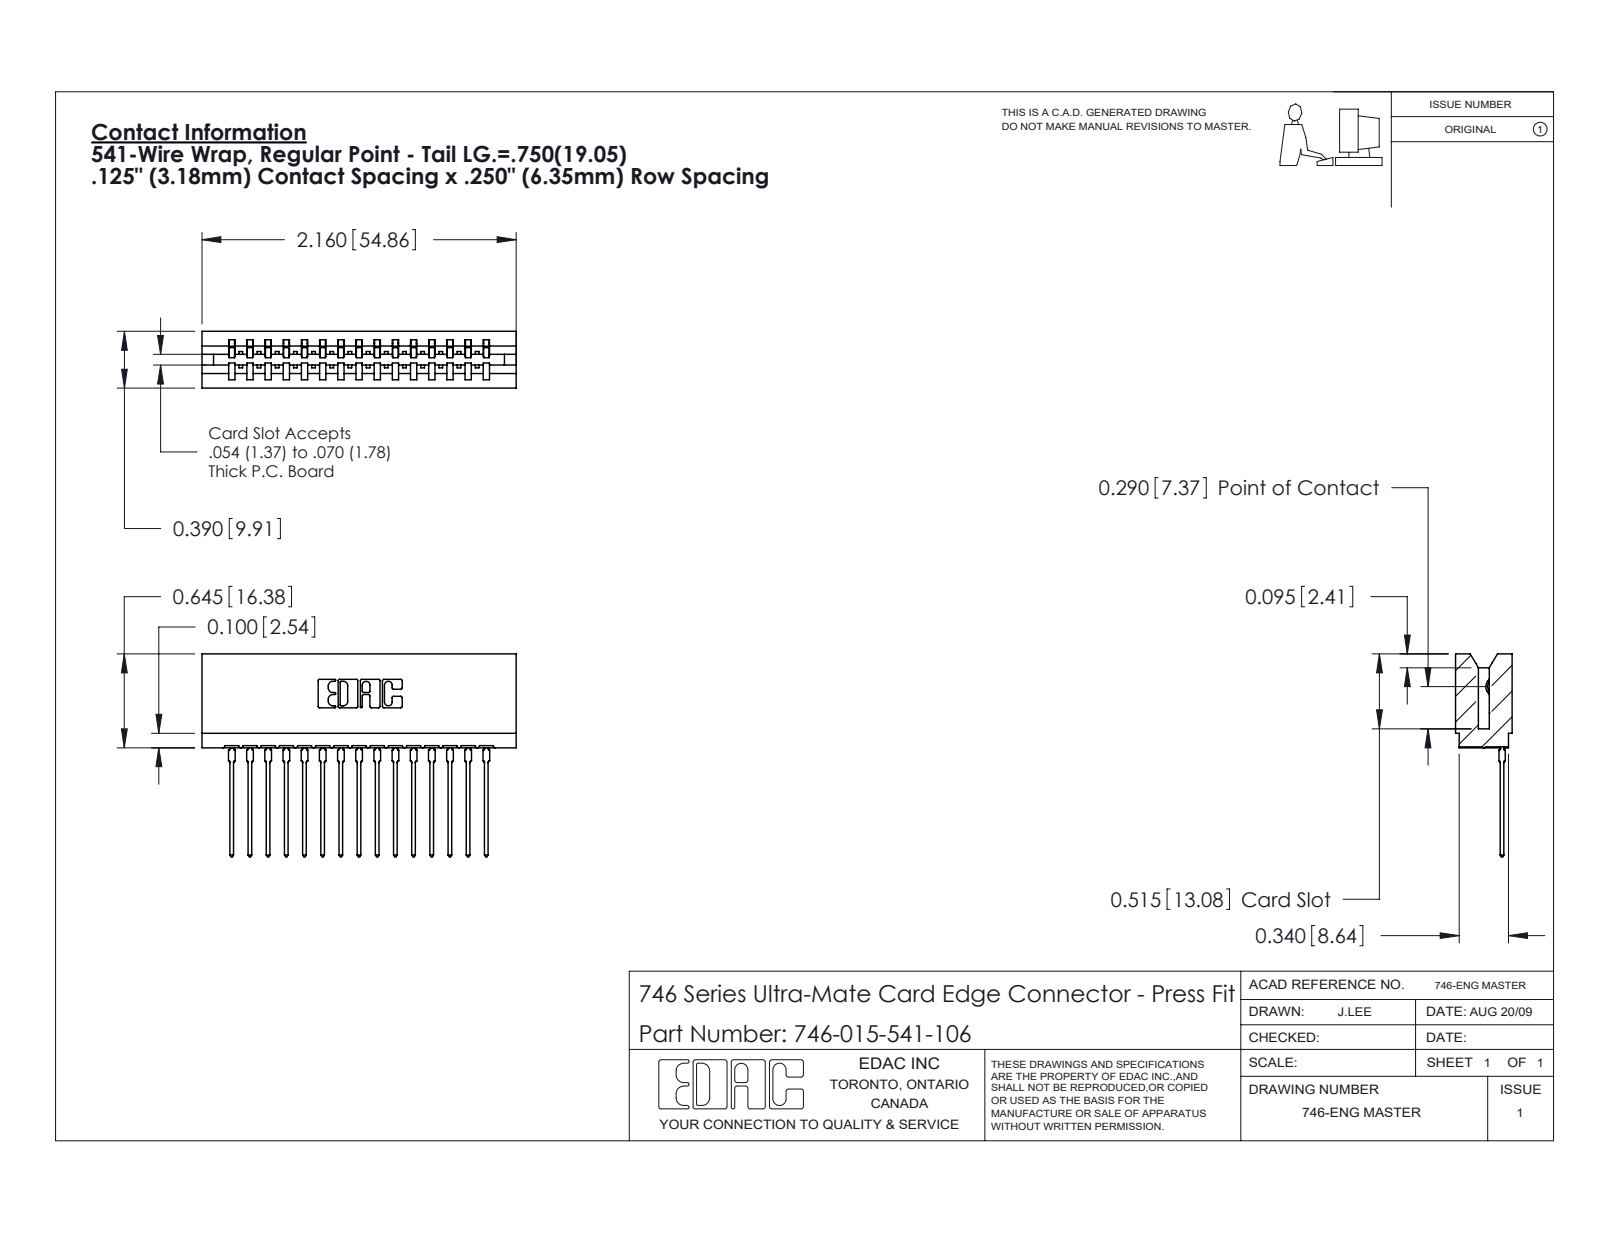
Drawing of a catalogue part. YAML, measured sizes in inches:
part_name: "746 Part_.515 Slot Depth - 06; 746-292-001_541; 746-015-541-106"
step_written_by: "SolidWorks 2020 (CONFIG_CONTROL_DESIGN)"
units: inches
bodies: {solids: 16, faces: 1718, planar: 1001, cylindrical: 327, other: 390}
overall_size: [2.16, 1.394, 0.39]
volume: 0.364
surface_area: 13.59
partial_cylinders:
  - {radius: 0.021, count: 30}
  - {radius: 0.01, count: 22}
  - {radius: 0.015, count: 16}
  - {radius: 0.007, count: 6}
  - {radius: 0.031, count: 6}
  - {radius: 0.005, count: 4}
  - {radius: 0.011, count: 4}
  - {radius: 0.026, count: 3}
face_to_face_distances: [0.25, 0.057, 0.333, 0.5, 0.39, 0.025, 0.307, 0.042, 0.125, 0.208]
